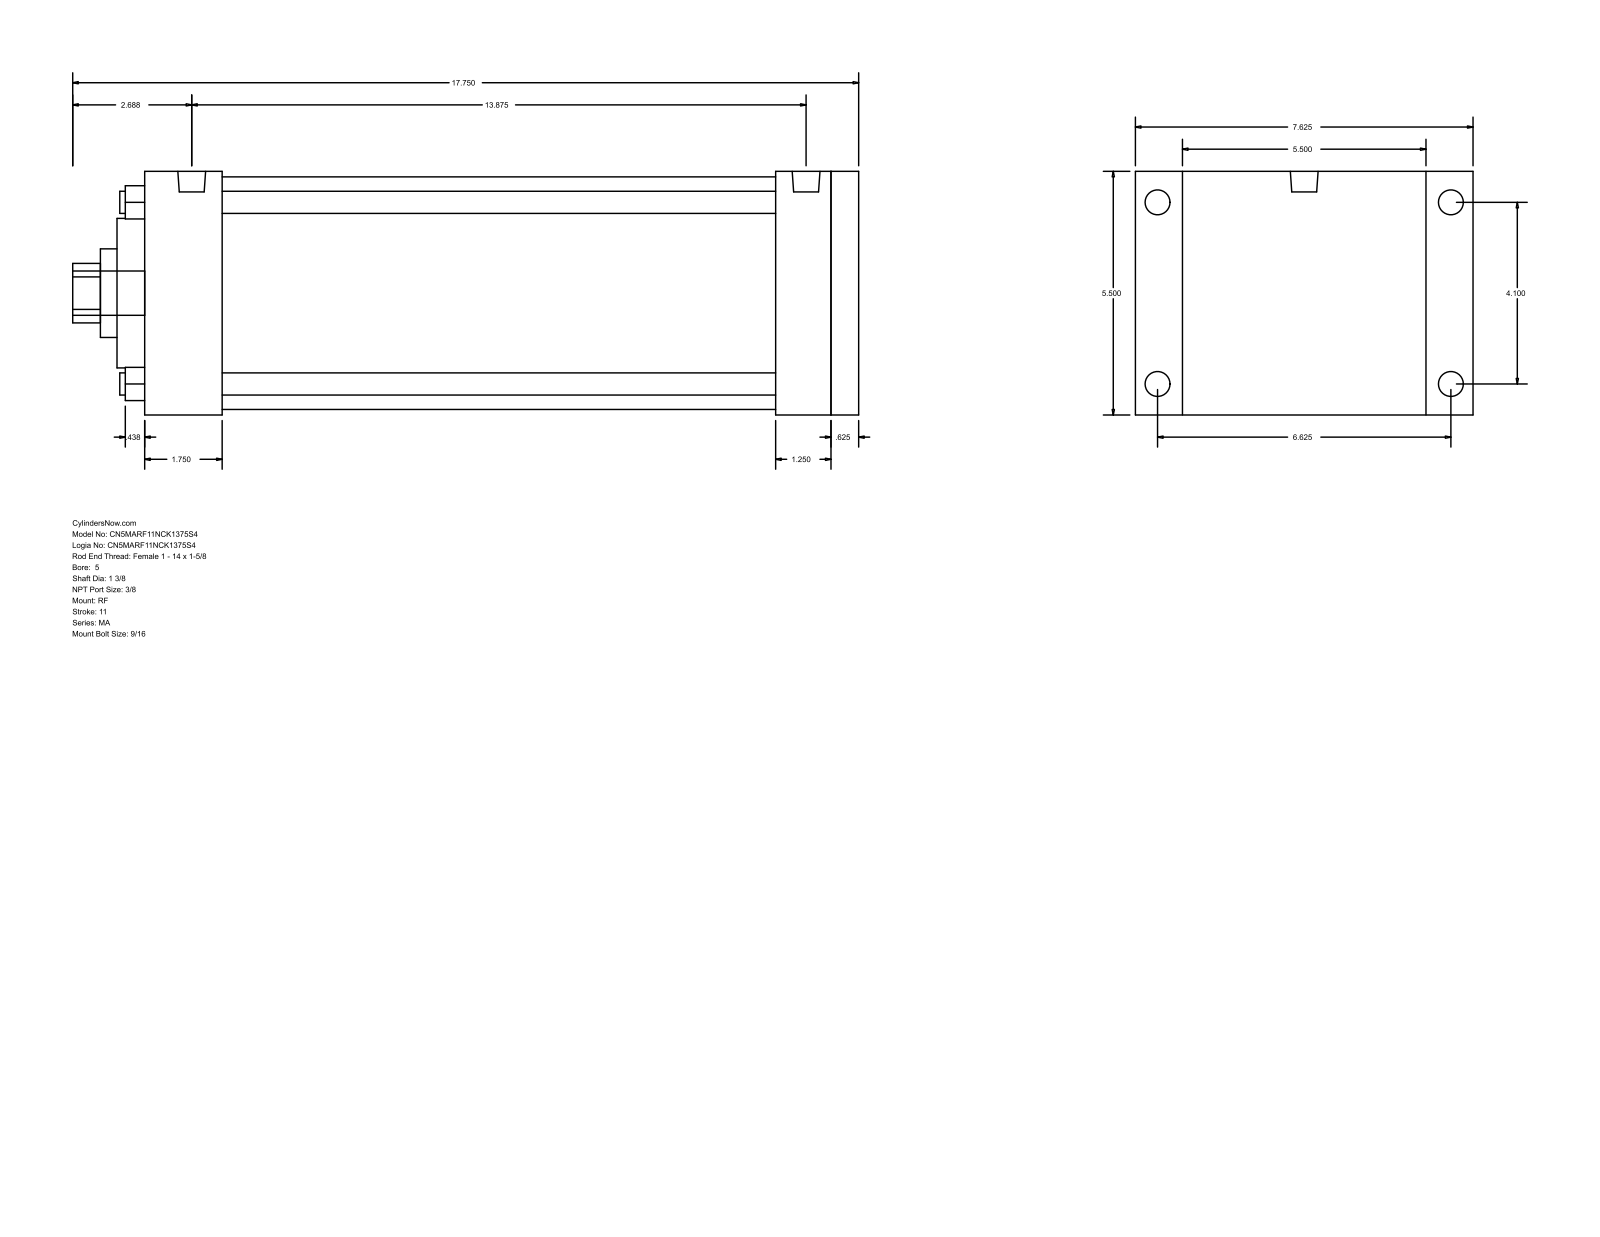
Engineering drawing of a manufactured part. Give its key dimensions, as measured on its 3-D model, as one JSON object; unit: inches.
{"part_name": "MA_RF__0500_1.375", "step_written_by": "GSSL Pune (CONFIG_CONTROL_DESIGN)", "units": "inches", "bodies": {"solids": 0, "faces": 94, "planar": 65, "cylindrical": 29, "other": 0}, "overall_size": [17.75, 7.625, 5.5], "round_holes": [[0.5, 4], [1.375, 1], [2, 1], [3.375, 1], [5.25, 1]], "round_bosses_or_shafts": [[0.563, 4], [0.437, 4], [0.627, 2], [1, 1]], "partial_cylinders_radius": [[0.672, 1]], "face_to_face_distances": [5.5, 16.125, 0.625, 15.5, 1.75, 13.75, 14.375, 14.25, 12.5, 1.25], "hole_center_spacings": [2.899, 4.1, 5.798]}
